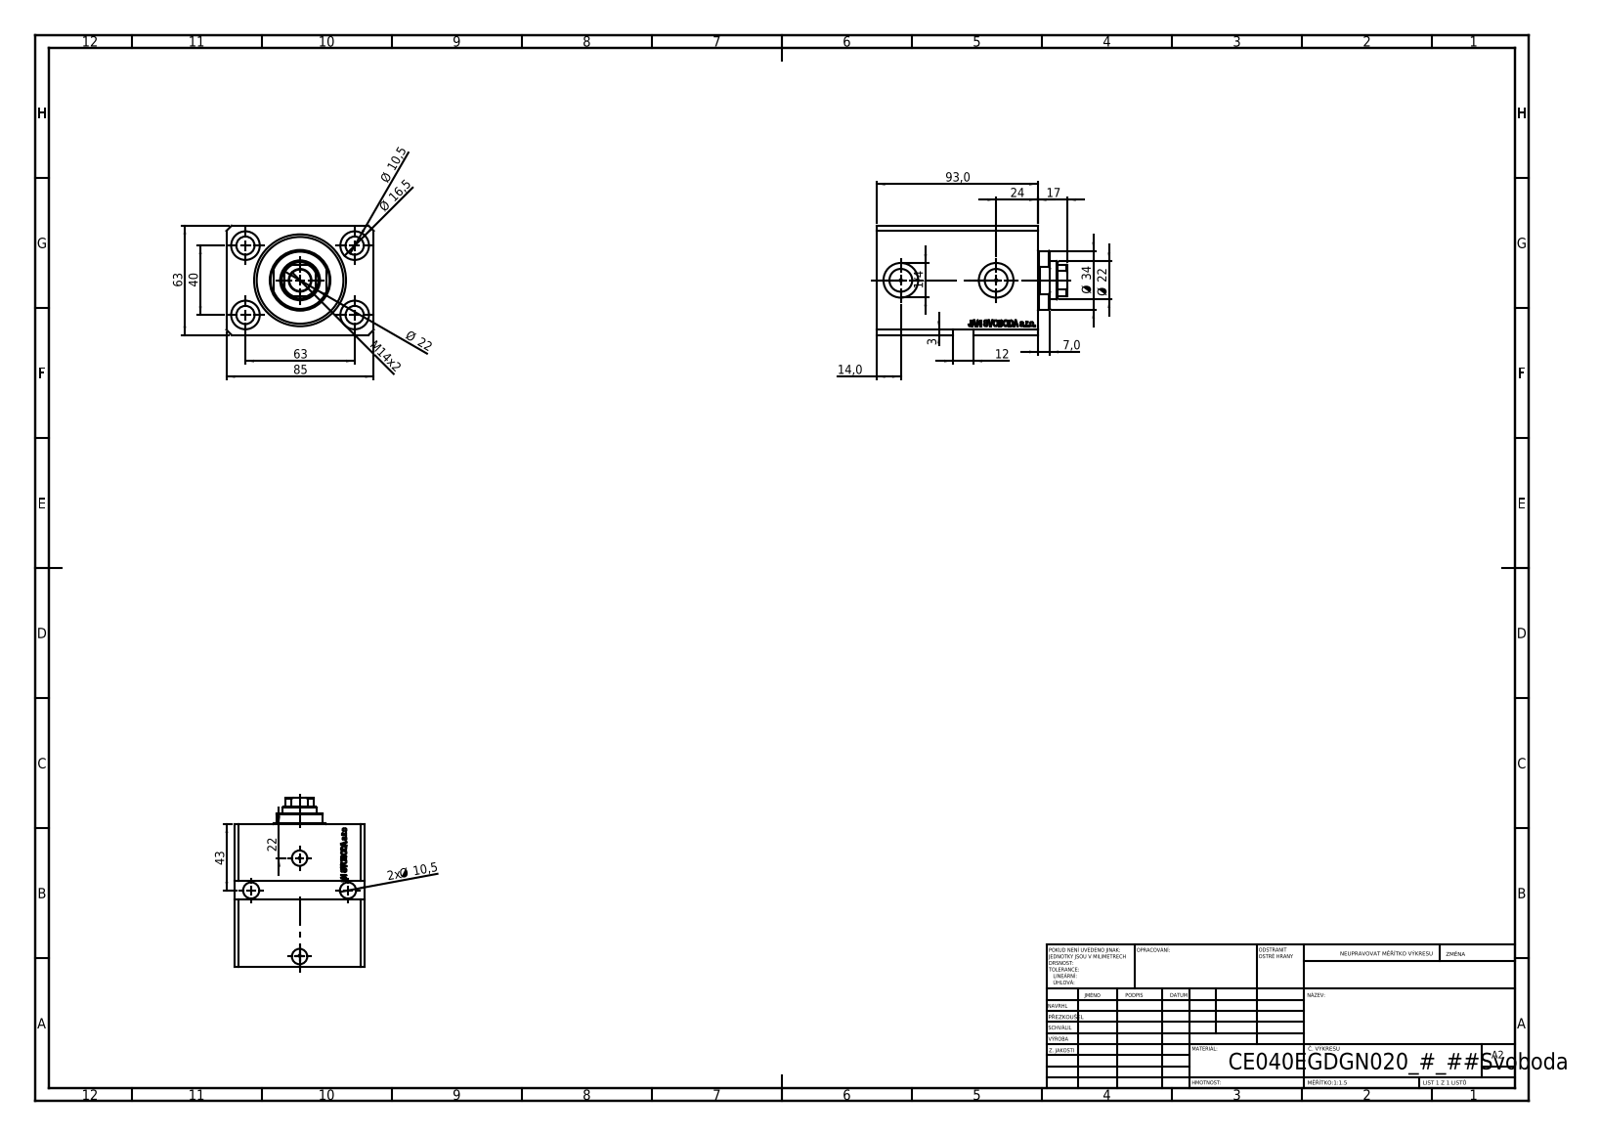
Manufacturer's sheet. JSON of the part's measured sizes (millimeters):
{"part_name": "V250CE_C_VCP; V250CE_E_Body; V250CE_VC_E", "step_written_by": "SolidWorks 2019 (CONFIG_CONTROL_DESIGN)", "units": "millimeters", "bodies": {"solids": 3, "faces": 933, "planar": 463, "cylindrical": 96, "other": 374}, "overall_size": [110, 85, 63], "volume_mm3": 423550, "surface_area_mm2": 88404, "round_holes": [[10.5, 6], [1.25, 4], [16.5, 4], [10, 2], [13.16, 2], [20, 2], [12.5, 1], [22, 1], [40, 1], [53, 1]], "round_bosses_or_shafts": [[34, 1]], "partial_cylinders_radius": [[10.5, 1]], "face_to_face_distances": [63, 85, 93, 17, 76, 11.4, 64.6, 81.6, 56, 44.6], "hole_center_spacings": [37.31, 63, 37.86, 40, 52.88, 53.3, 74.63, 0.53]}
